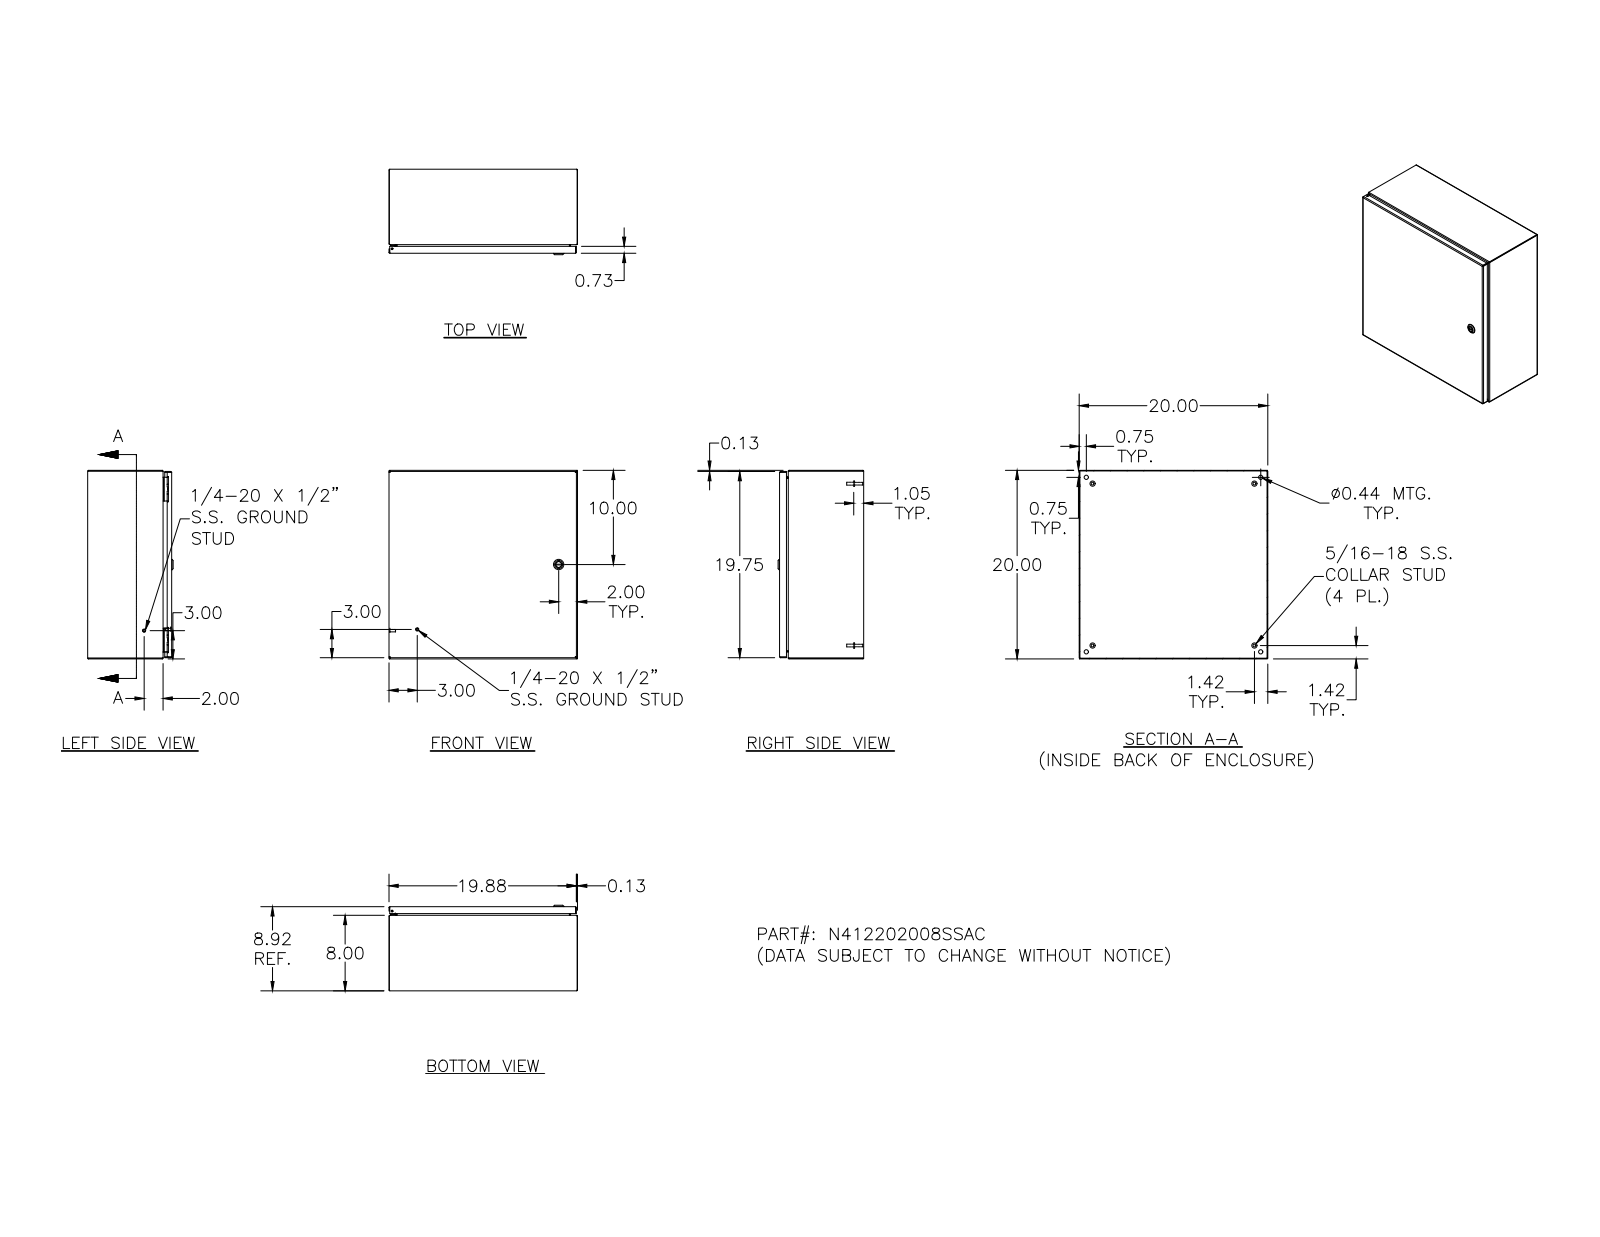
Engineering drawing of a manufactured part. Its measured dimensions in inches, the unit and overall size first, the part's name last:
Units: inches
Overall size (bounding box): 20 × 20 × 9.075
Round holes (diameter × count): ⌀0.188 ×5, ⌀0.093 ×4, ⌀0.152 ×4, ⌀0.167 ×4, ⌀0.172 ×4, ⌀0.437 ×4, ⌀0.156 ×2, ⌀0.187 ×1, ⌀0.197 ×1, ⌀0.315 ×1, ⌀0.394 ×1, ⌀0.402 ×1
Round bosses / shafts (diameter × count): ⌀0.25 ×10, ⌀0.563 ×4, ⌀0.36 ×4, ⌀0.32 ×4, ⌀0.3 ×4, ⌀0.275 ×4, ⌀0.256 ×4, ⌀0.164 ×4
Partial cylindrical surfaces — rounded edges, fillets, slot ends (radius × count): R0.05 ×26, R0.016 ×18, R0.016 ×16, R0.09 ×16, R0.031 ×14, R0.125 ×14, R0.02 ×9, R0.032 ×8
Main face-to-face distances: 0.074, 8.843, 19.926, 8.769, 8.917, 20, 19.852, 7.926, 0.917, 0.739
Hole centre spacings: 16, 0.017, 0.66, 16.008, 18.5, 18.872, 0.019, 0.5
Volume: 118.7 in³ · Surface area: 3 228 in²
Bodies: 34 solids, 1364 faces (523 planar, 497 cylindrical, 344 other)
Part name (STEP PRODUCT): N412202008SSAC; N412202008SSACBKP; 388151; N4122020SSACLID (+8 more)
STEP written by: Autodesk Inventor 2011 (AUTOMOTIVE_DESIGN)
